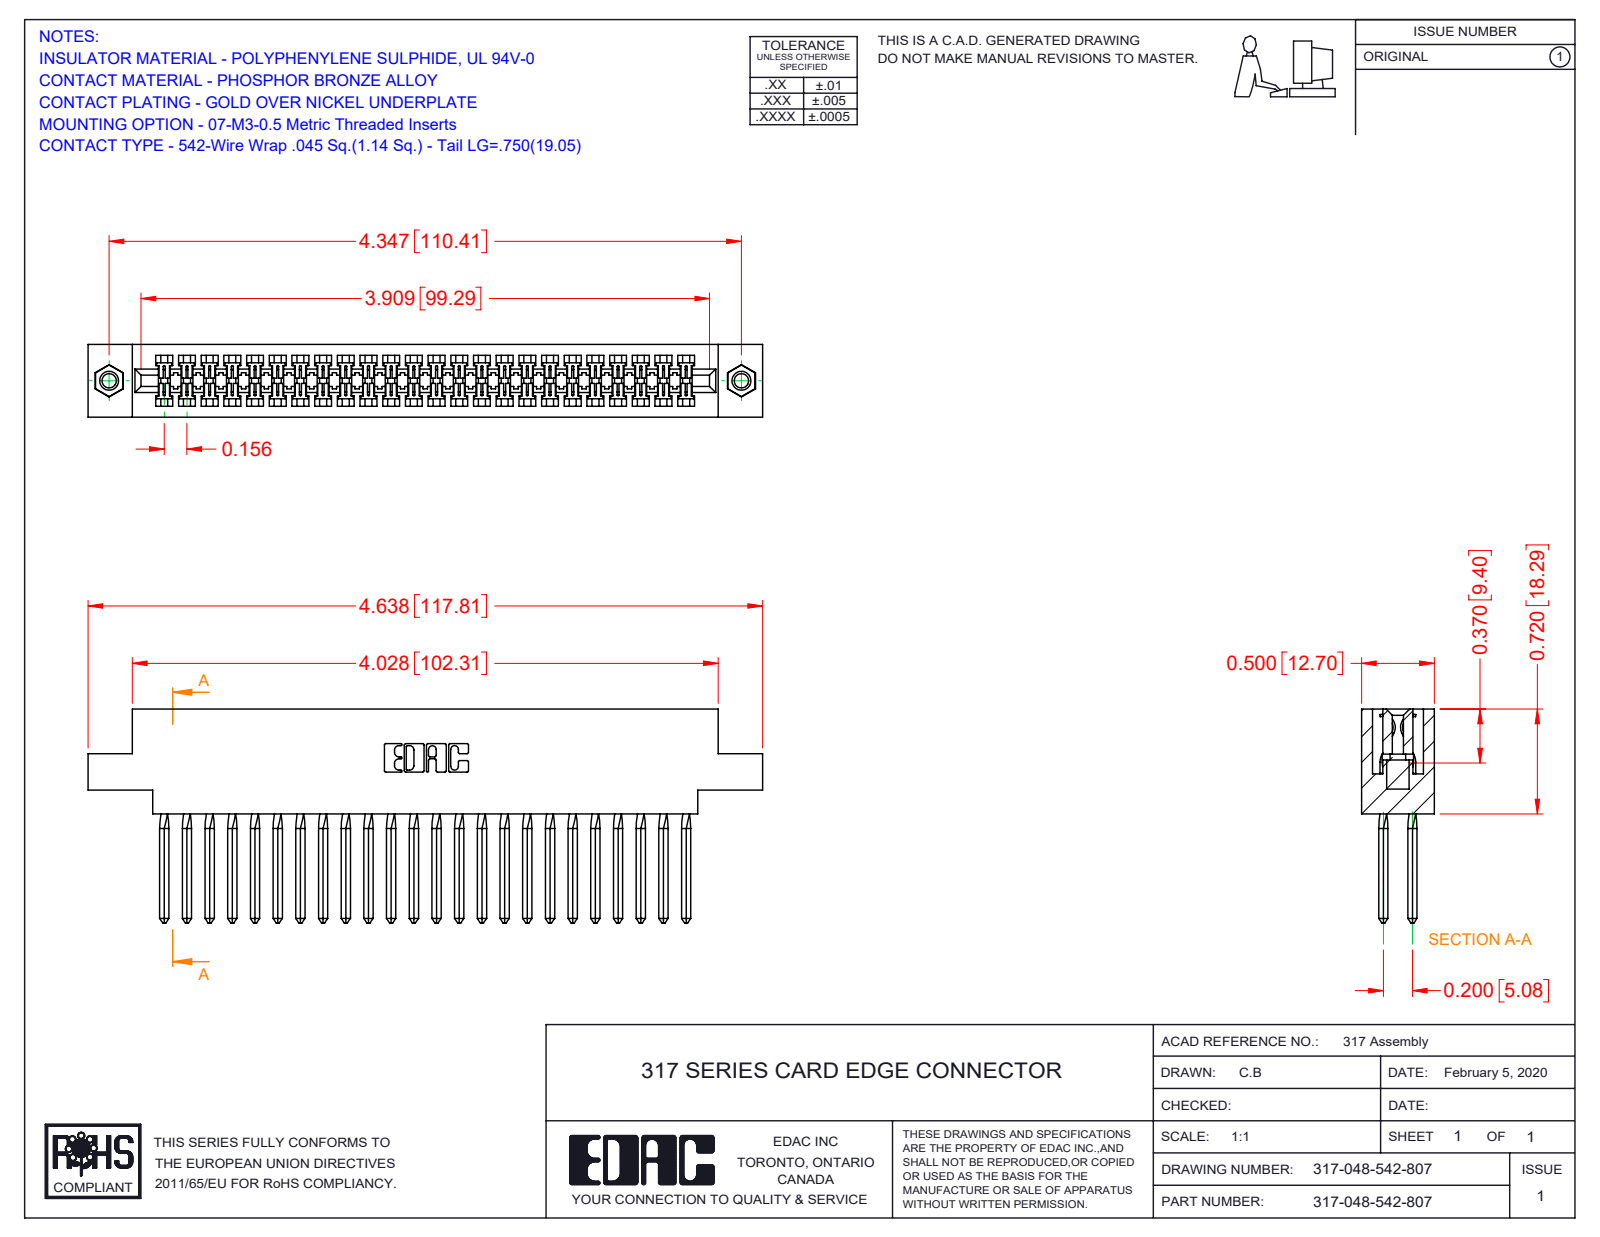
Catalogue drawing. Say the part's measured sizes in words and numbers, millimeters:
The part is named "317-048-542-807; 345-250-001_345-250-005-103; 317 Part_.156 Dia - TI; 317-290-003_542". Its 3-D file was written by "SolidWorks 2016 (CONFIG_CONTROL_DESIGN)". It is 51 solids with 2898 faces: 2298 planar, 392 cylindrical and 208 other. Overall it measures 117.8 by 37.3 by 12.7 millimeters. Its volume is 18 710 cubic millimeters and its surface area 25 470 square millimeters. Round holes: 2 of diameter 2.5, 2 of diameter 3.2, 2 of diameter 4. Round bosses or shafts: 2 of diameter 3.9. Partial cylindrical surfaces (rounded edges, fillets, slot ends): 96 of radius 0.2, 22 of radius 0.3, 6 of radius 0.2, 6 of radius 0.8, 3 of radius 0.7, 2 of radius 1.9, 2 of radius 2.3, 2 of radius 2.5. The main face-to-face distances are 12.7, 1.9, 10.8, 8.9, 2.8, 5.1, 2.9, 3.5, 1.2, 18.3. The hole center spacings are 110.4.
